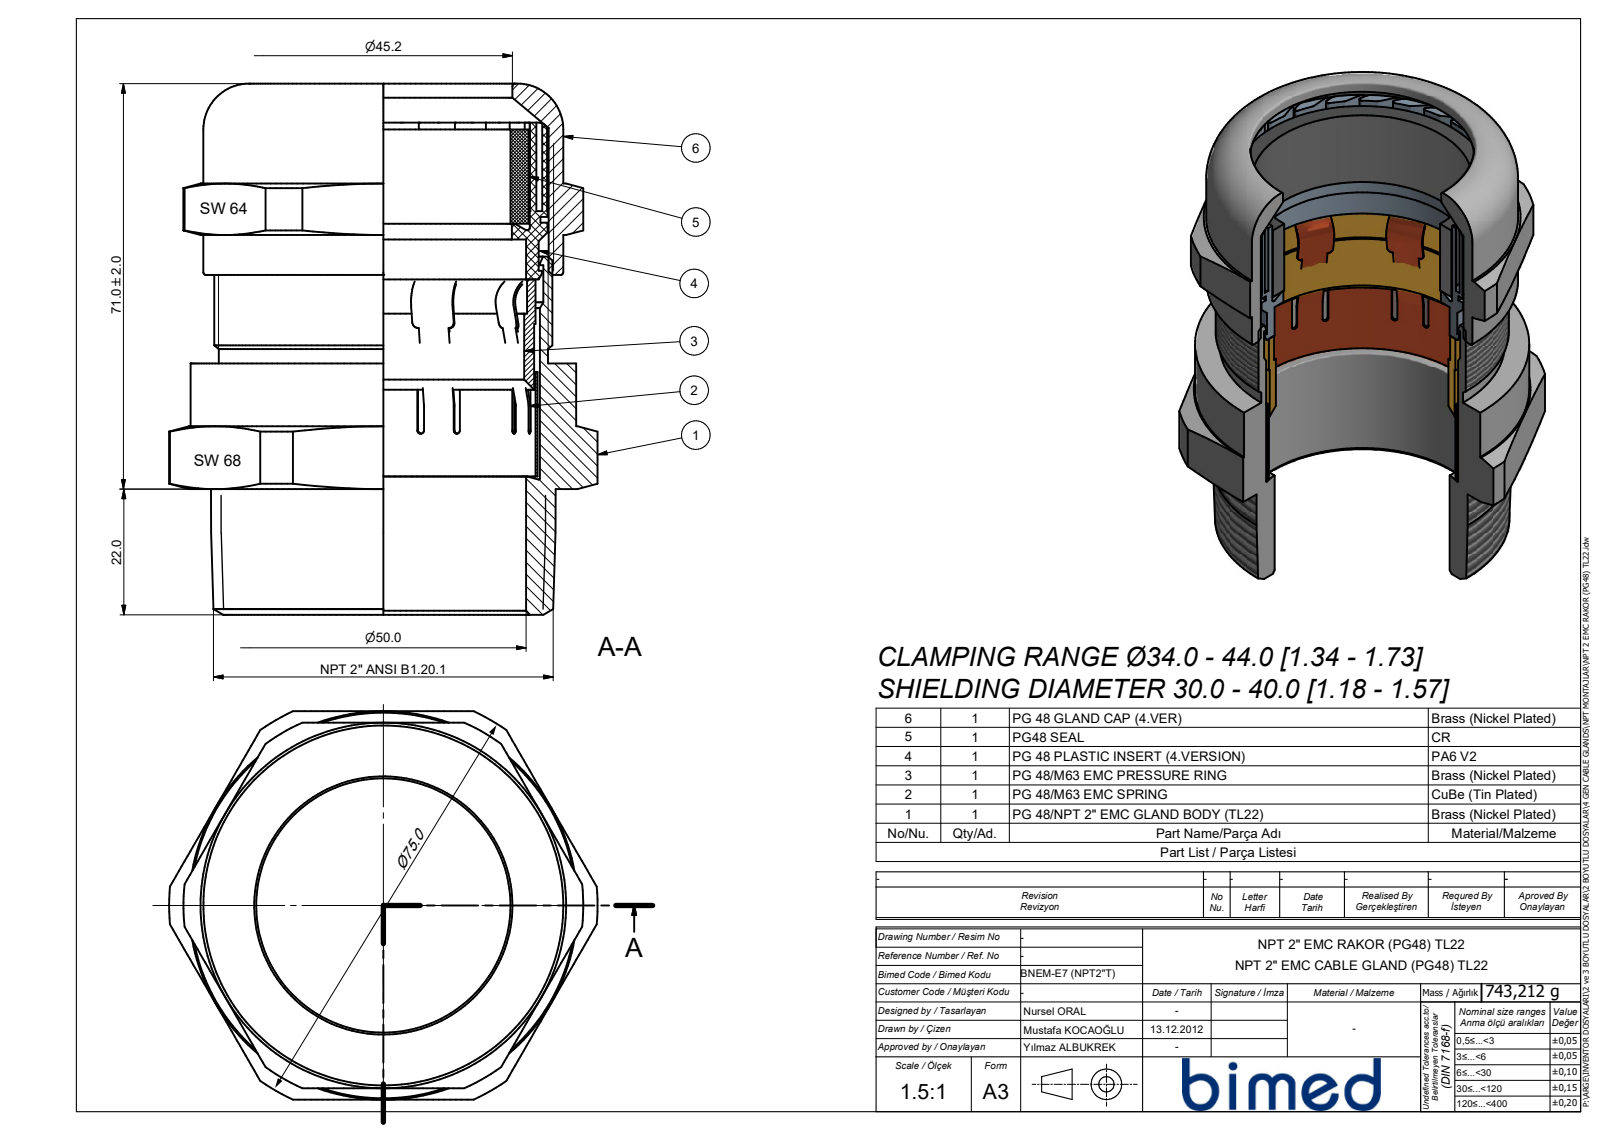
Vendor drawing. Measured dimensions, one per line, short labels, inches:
name: BNEM-E7-2T-WCL
written by: SolidWorks 2021 (CONFIG_CONTROL_DESIGN)
unit: in
bodies: 1 solid, 78 faces (20 planar, 22 cylindrical, 36 other)
size: 3.661 × 2.953 × 2.677
volume: 17.83 in³; area: 41.89 in²
bosses: 1× ⌀2.657, 1× ⌀2.48, 1× ⌀2.331, 1× ⌀2.269
rounds: 1× R1.378, 1× R1.476
face distances: 3.661, 0.866, 0.079, 2.598, 2.677, 1.732, 1.928, 2.794, 2.52, 2.342
